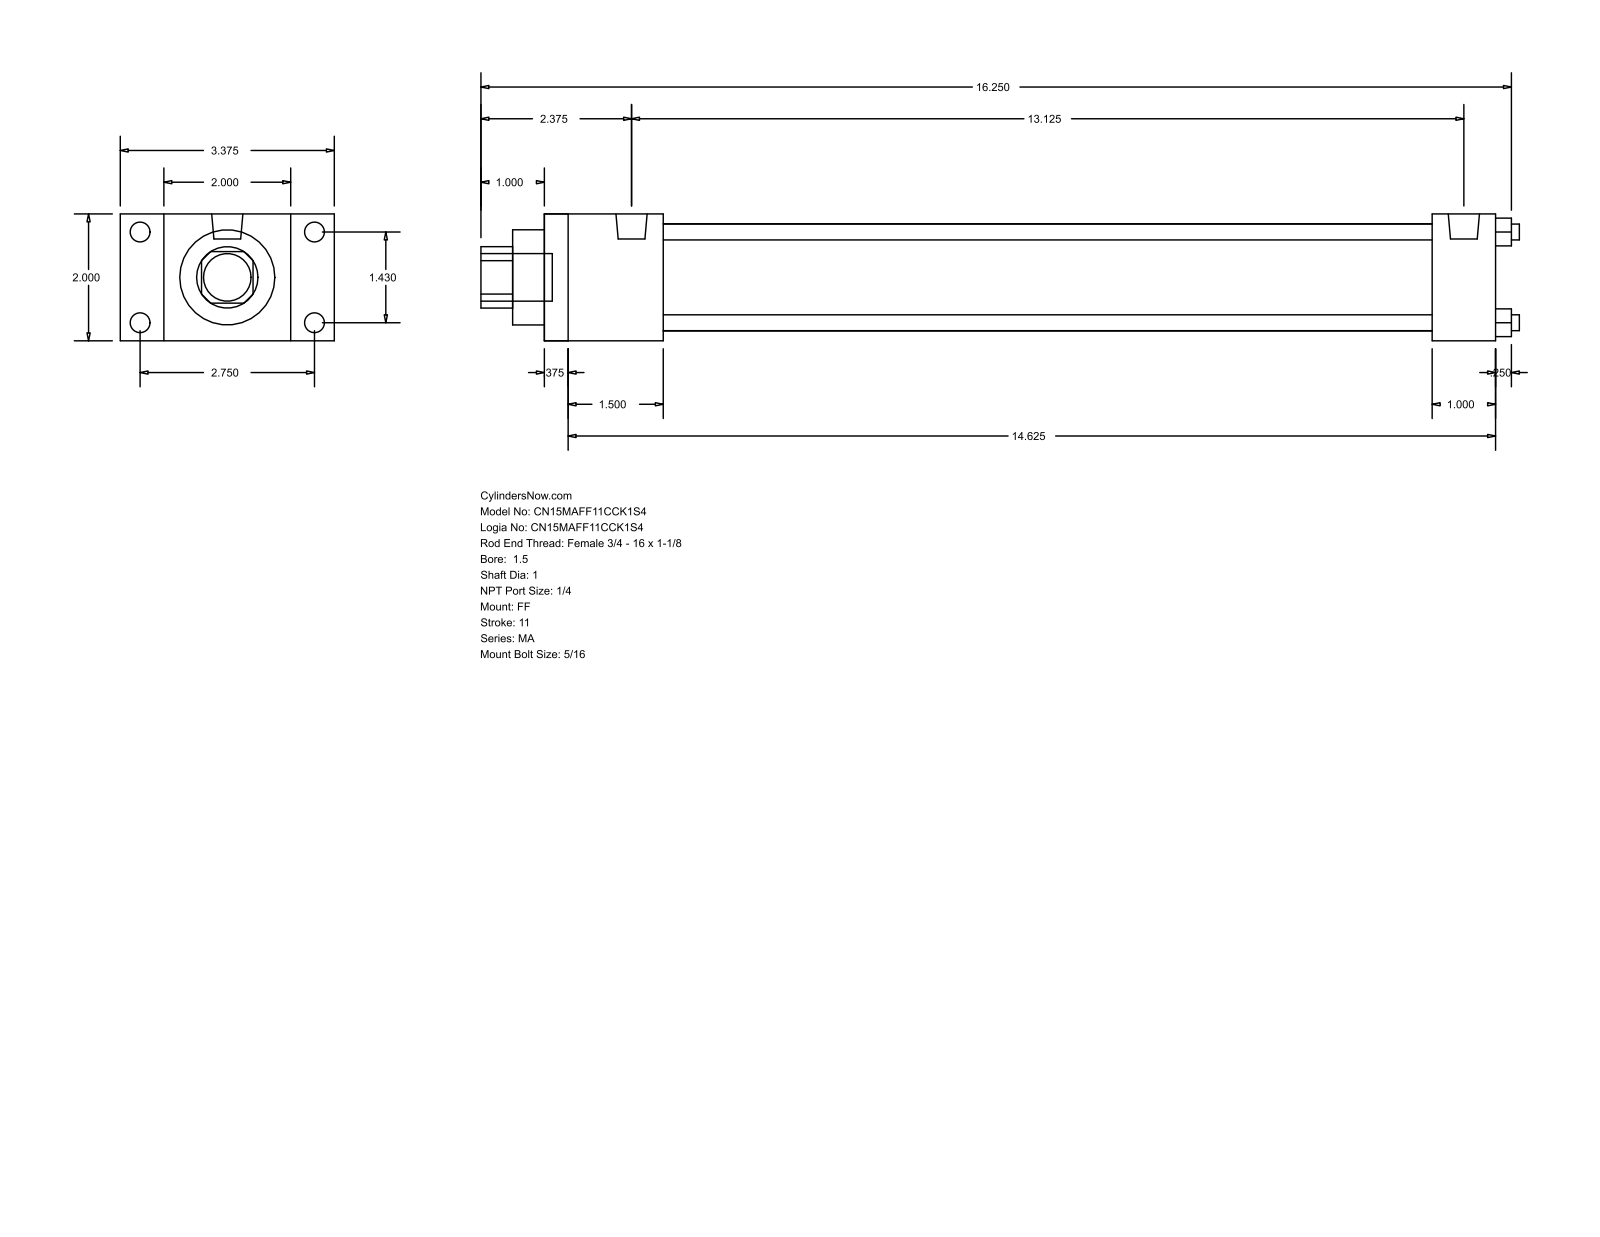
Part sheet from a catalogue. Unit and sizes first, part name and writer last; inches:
Units: inches
Overall size (bounding box): 16.375 × 3.375 × 2
Round holes (diameter × count): ⌀0.25 ×4, ⌀1 ×1, ⌀1.5 ×1, ⌀1.69 ×1
Round bosses / shafts (diameter × count): ⌀0.313 ×8, ⌀0.492 ×2, ⌀0.75 ×1
Partial cylindrical surfaces — rounded edges, fillets, slot ends (radius × count): R0.484 ×1
Main face-to-face distances: 2, 15, 0.375, 14.625, 1, 1.875, 14, 1.5, 13.625, 12.125
Hole centre spacings: 1.011, 1.43, 2.022
Bodies: 0 solids, 92 faces (64 planar, 28 cylindrical, 0 other)
Part name (STEP PRODUCT): MA_FF__0150_1
STEP written by: GSSL Pune (CONFIG_CONTROL_DESIGN)
